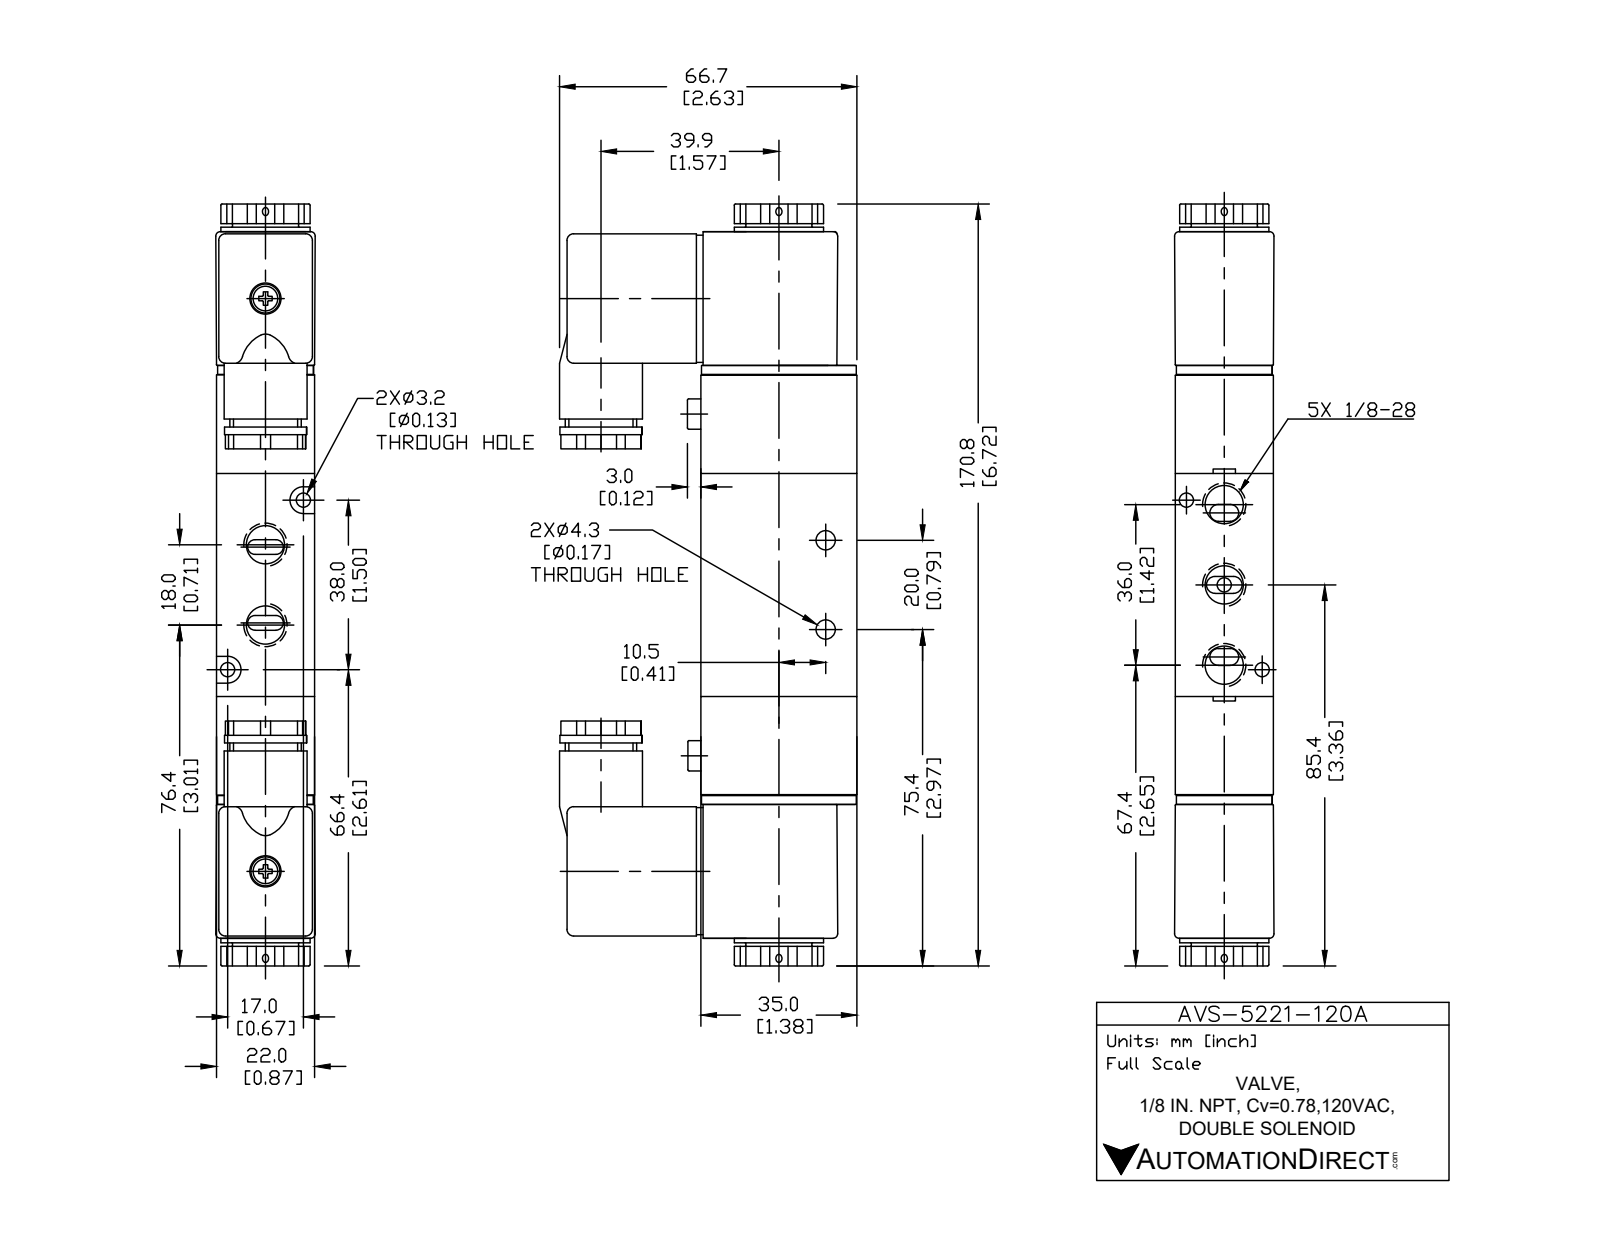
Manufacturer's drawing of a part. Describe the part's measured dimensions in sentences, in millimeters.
The part is named "AVS-5221-120A". Its 3-D file was written by "SolidWorks 2015 (CONFIG_CONTROL_DESIGN)". It is 5 solids with 278 faces: 133 planar, 111 cylindrical and 34 other. Overall it measures 170.8 by 66.7 by 22 millimeters. Its volume is 158 275 cubic millimeters and its surface area 35 246 square millimeters. Round holes: 5 of diameter 8.43, 2 of diameter 4.3, 1 of diameter 3.2, 1 of diameter 3.3, 1 of diameter 9.3. Round bosses or shafts: 2 of diameter 6.7, 1 of diameter 20, 1 of diameter 18.6, 1 of diameter 18.4, 1 of diameter 16, 1 of diameter 14.8. Partial cylindrical surfaces (rounded edges, fillets, slot ends): 18 of radius 1.5, 10 of radius 1, 10 of radius 1.54, 8 of radius 0.5, 2 of radius 3. The main face-to-face distances are 0.5, 22, 21.5, 35, 22.88, 21, 50, 30, 65, 53.7. The hole center spacings are 9, 18, 8.56, 13.12, 20.81, 27, 29.26, 37.96.
